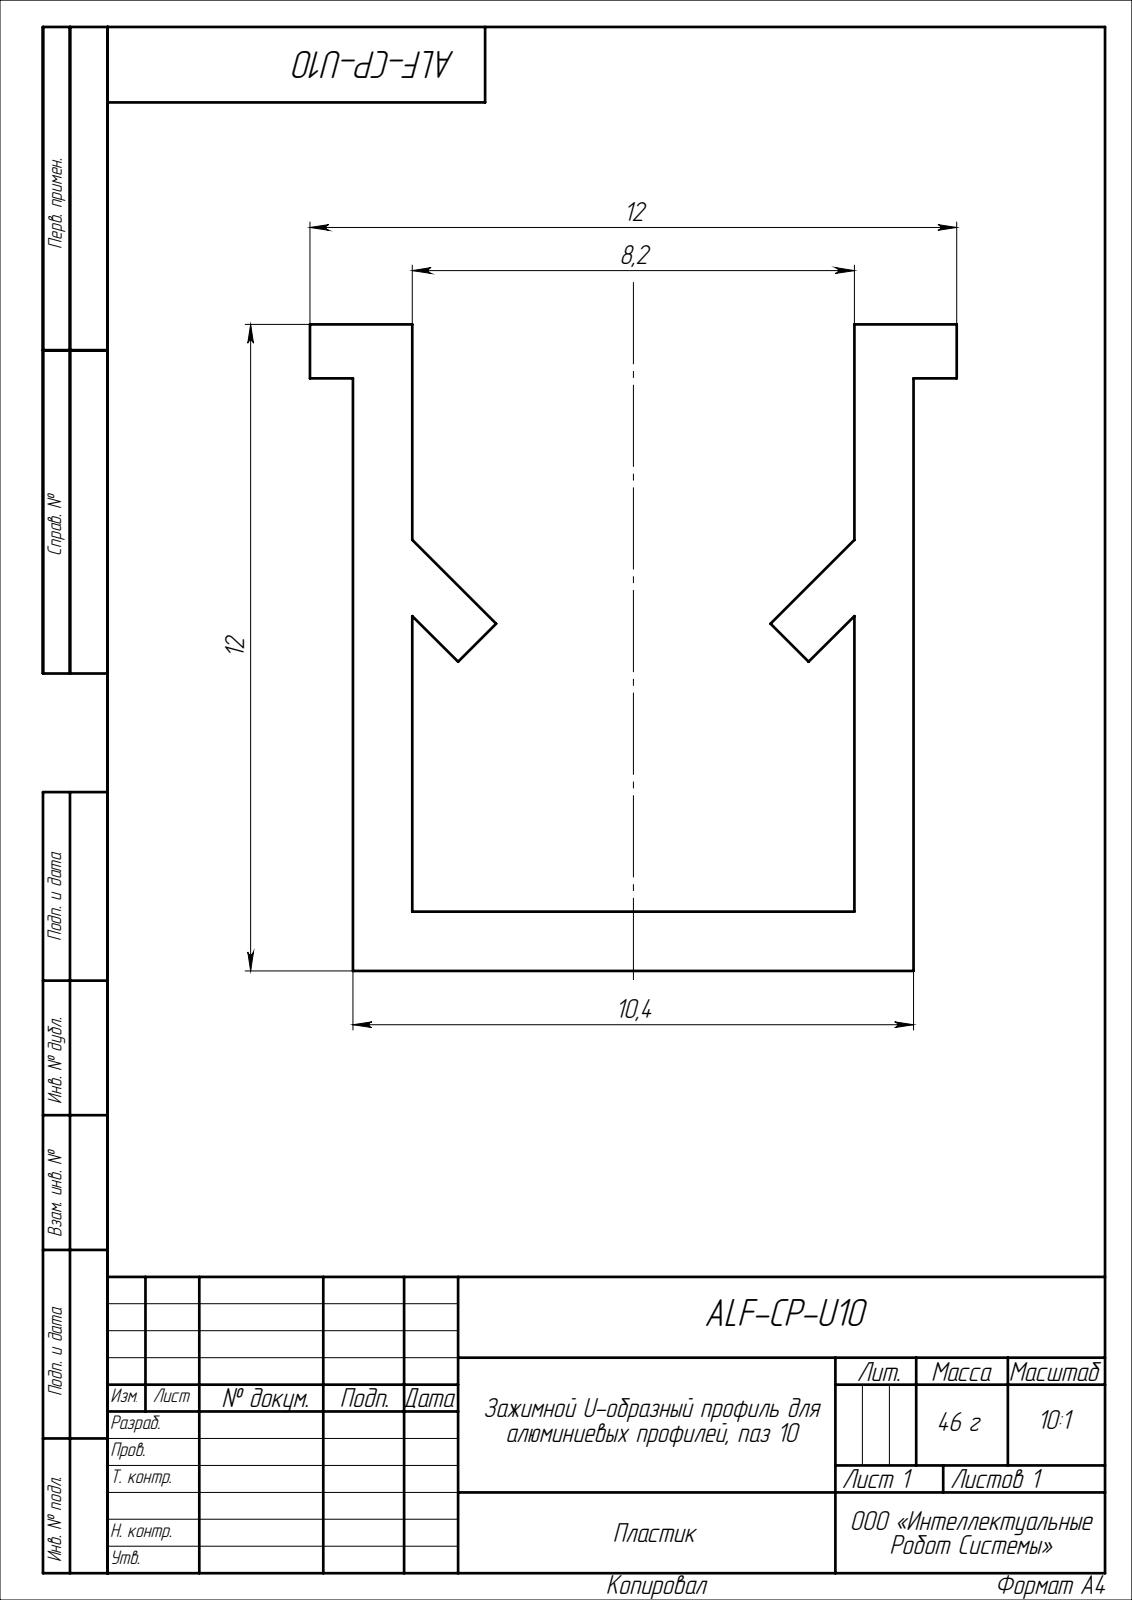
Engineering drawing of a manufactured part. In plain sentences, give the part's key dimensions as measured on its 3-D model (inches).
The part is named "ALF-CP-U10". Its 3-D file was written by "SolidWorks 2022 (CONFIG_CONTROL_DESIGN)". It is 1 solid with 22 faces: 22 planar, 0 cylindrical and 0 other. Overall it measures 39.37 by 0.472 by 0.472 inches. Its volume is 2.467 cubic inches and its surface area 117.6 square inches. The main face-to-face distances are 0.043, 0.366, 0.409, 0.323, 0.472, 0.039, 0.429, 0.142, 0.181, 0.031.
